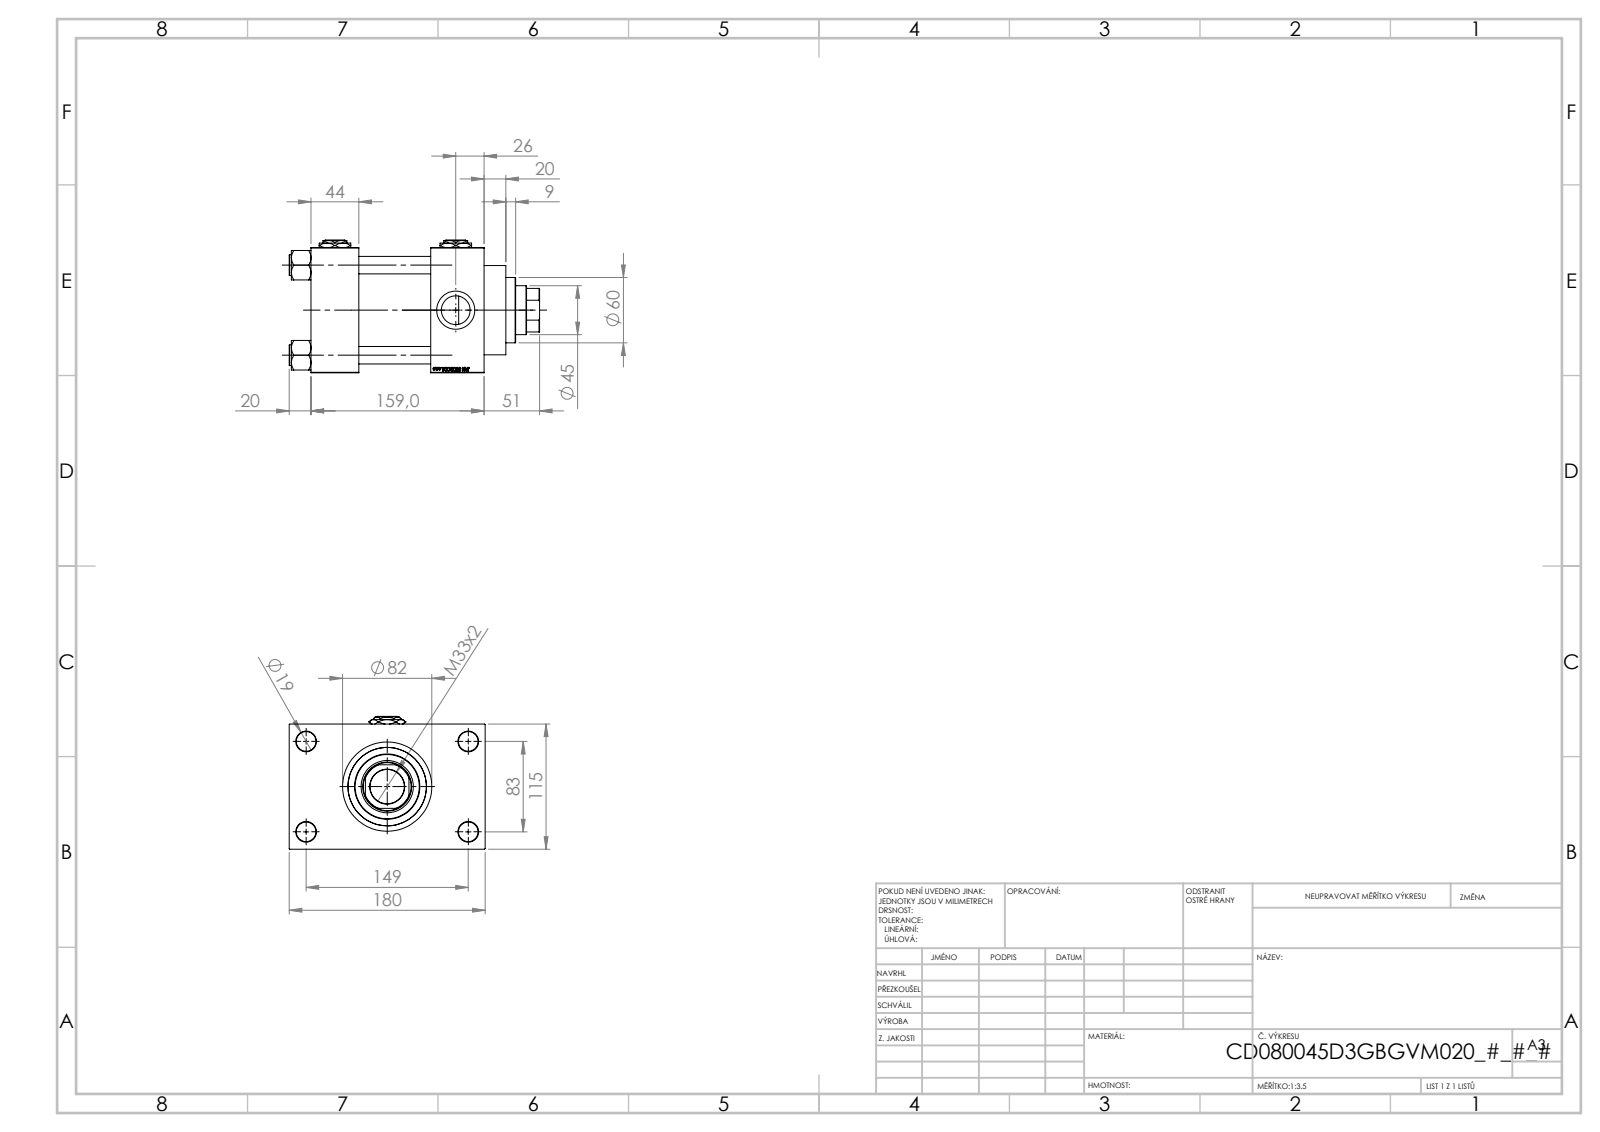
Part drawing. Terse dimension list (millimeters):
name: V215CD_D_Body; V215CD_NUT_M5_D; V215CD_VCP_D; V215CD_D_TYCINKA (+2 more)
written by: SolidWorks 2019 (CONFIG_CONTROL_DESIGN)
unit: mm
bodies: 13 solids, 1252 faces (593 planar, 99 cylindrical, 560 other)
size: 230 × 180 × 122
volume: 1 991 000 mm³; area: 309 018 mm²
holes: 4× ⌀16, 4× ⌀18, 4× ⌀26.44, 4× ⌀35, 3× ⌀7, 1× ⌀31.5, 1× ⌀45, 1× ⌀48, 1× ⌀61, 1× ⌀72, 1× ⌀80
bosses: 4× ⌀19, 1× ⌀86, 1× ⌀82, 1× ⌀60
rounds: 1× R22
face distances: 115, 110, 66, 49, 44, 159, 147.5, 32.5, 20, 69
hole spacings: 33.15, 58.48, 82.7, 85.28, 89.24, 115.85, 142.43, 83
